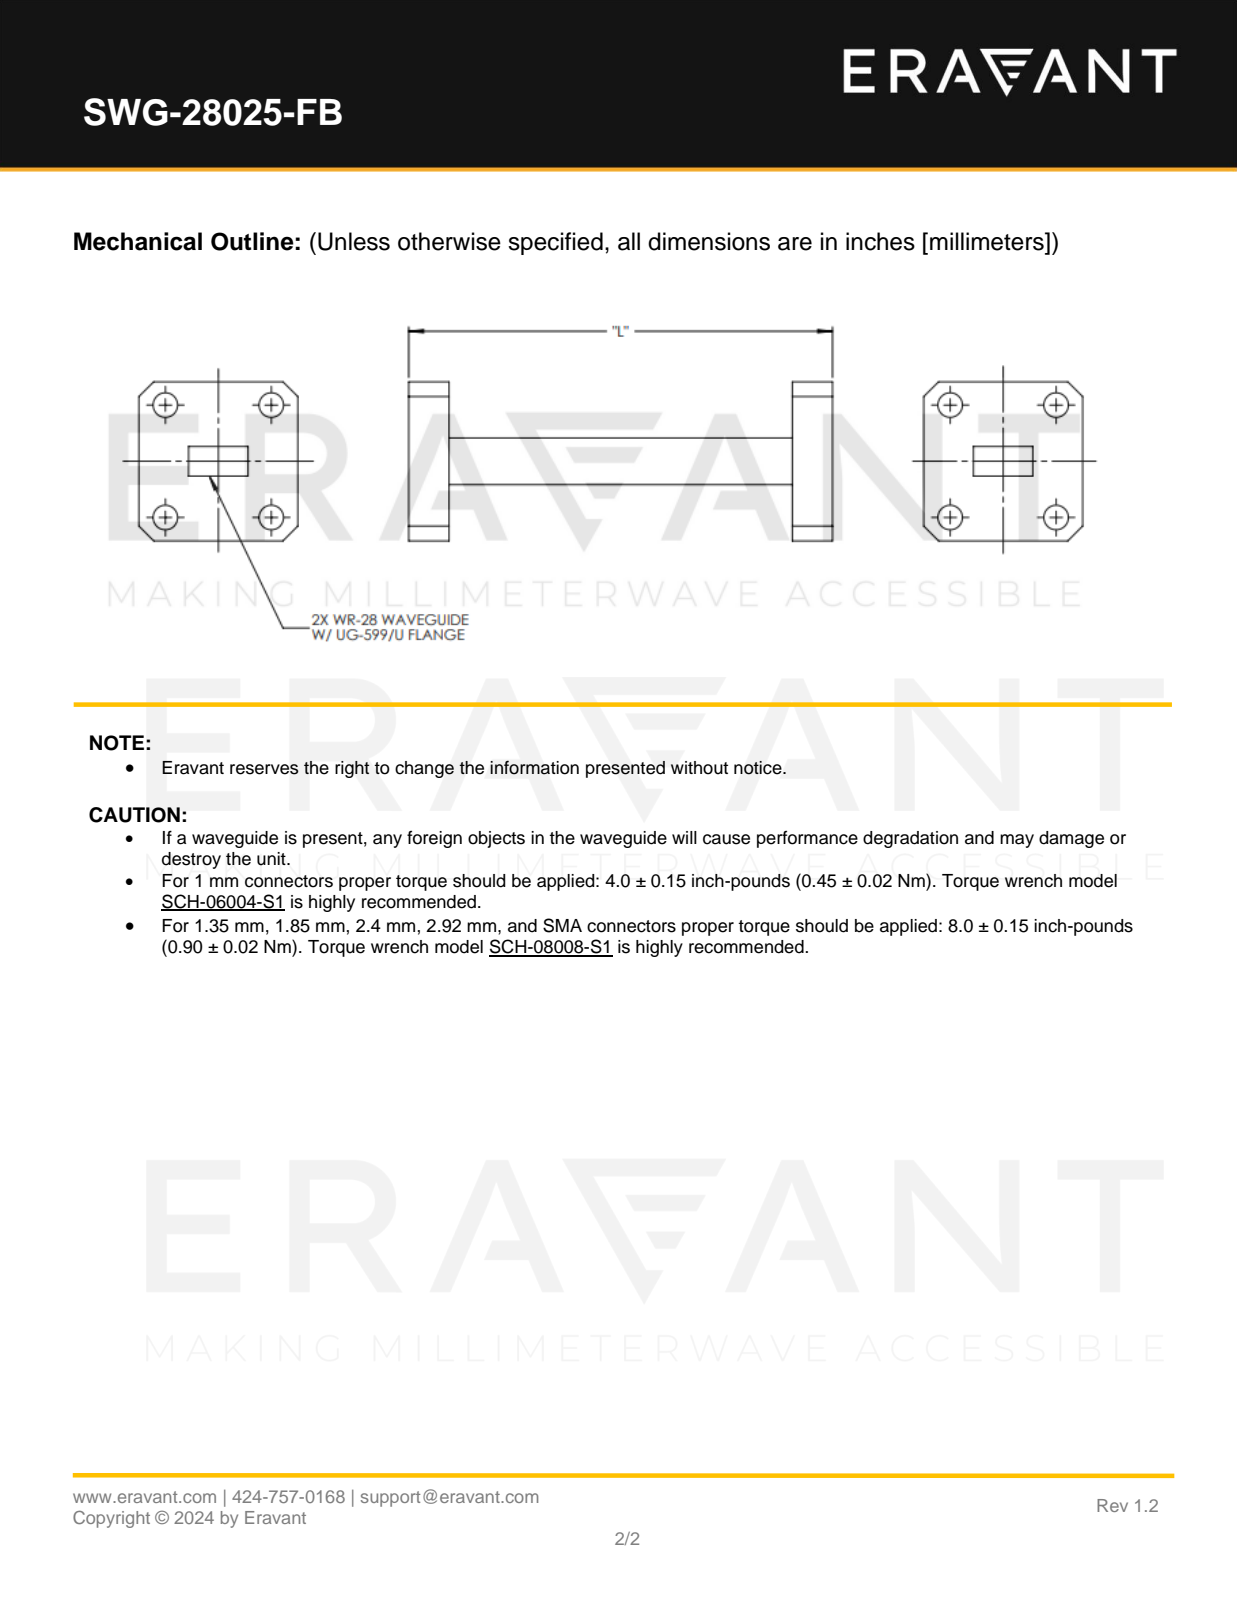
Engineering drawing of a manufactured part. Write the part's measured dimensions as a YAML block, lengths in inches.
part_name: "SWG-28025-FB"
step_written_by: "SolidWorks 2021 (CONFIG_CONTROL_DESIGN)"
units: inches
bodies: {solids: 1, faces: 50, planar: 34, cylindrical: 16, other: 0}
overall_size: [2.5, 0.75, 0.75]
volume: 0.361
surface_area: 5.991
round_holes:
  - {diameter: 0.116, count: 4}
face_to_face_distances: [0.19, 2.31, 0.22, 2.5, 0.36, 2.12, 0.75, 0.195, 0.555, 0.265]
hole_center_spacings: [0.5, 0.53, 0.729]
